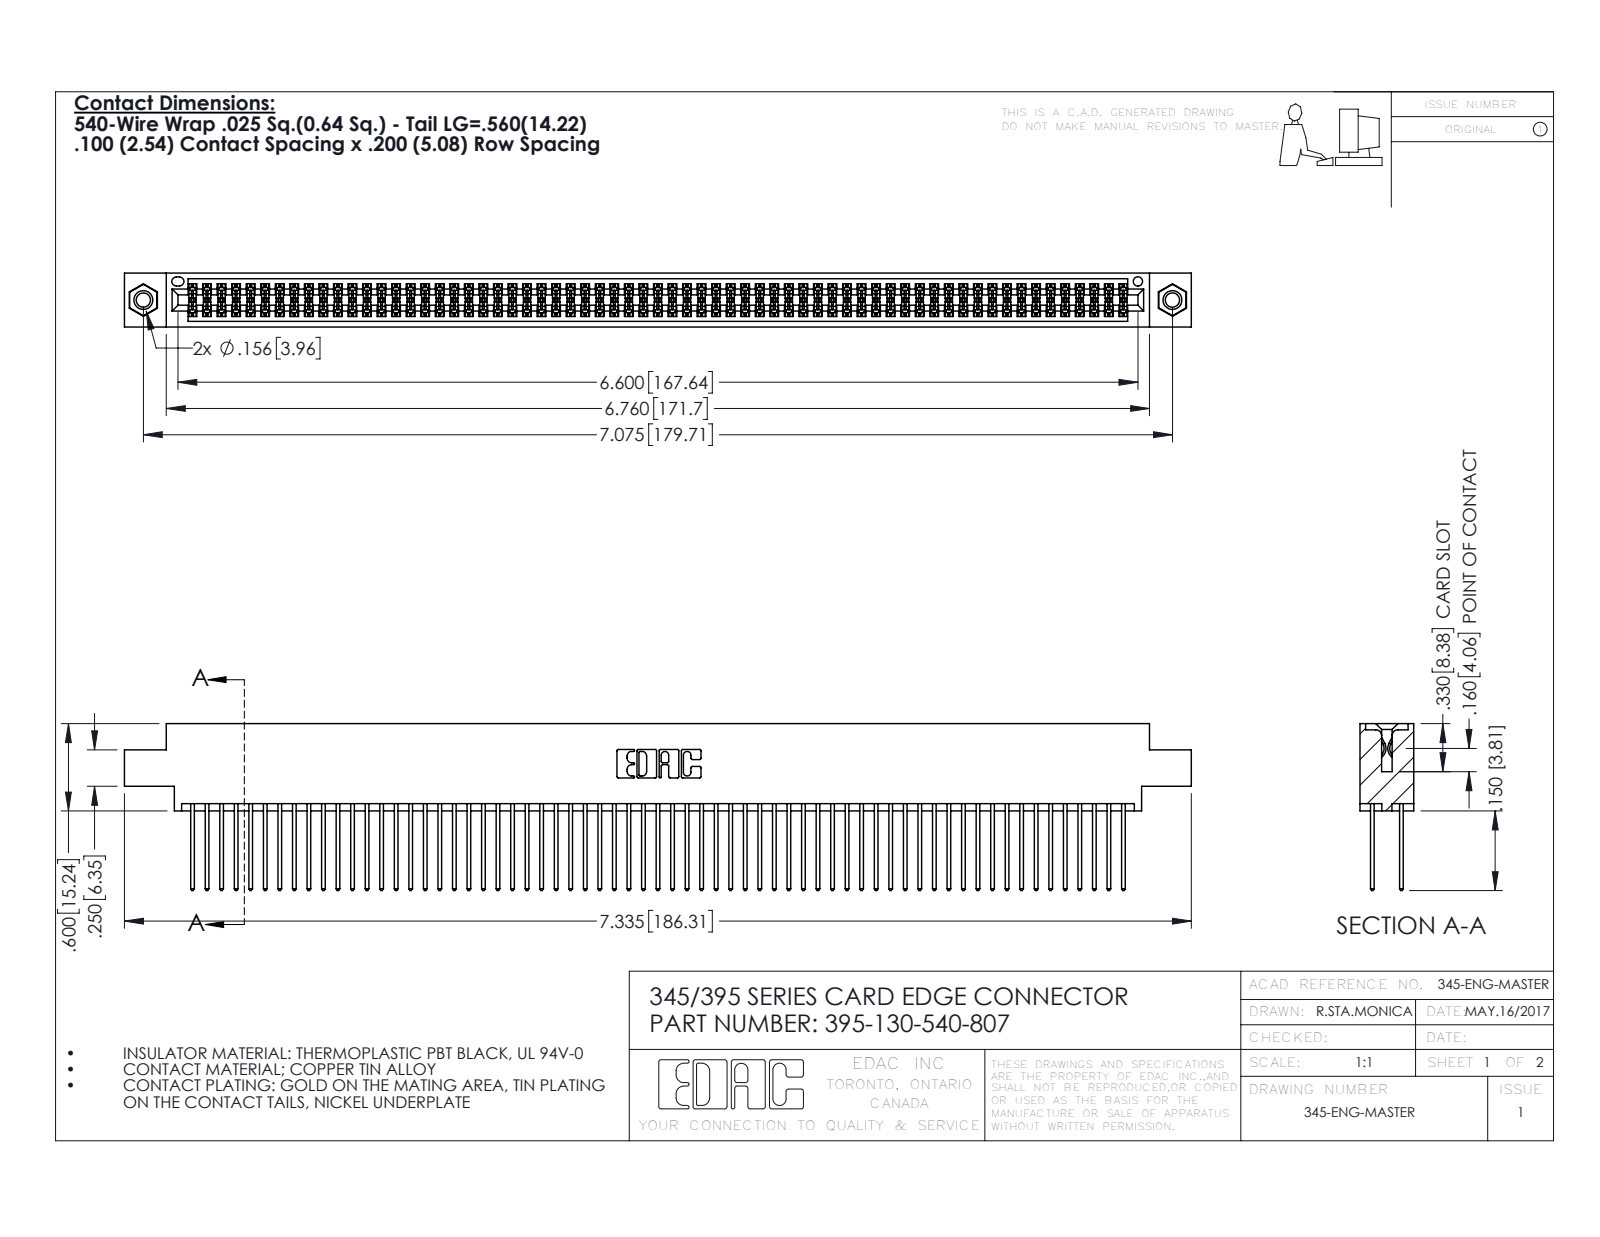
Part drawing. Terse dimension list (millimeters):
name: 345-292-001_345-293-140; 395-130-540-807; 345 Part_0.170 Offset - 0.156 Dia-TI; 345-250-001_345-250-005-103
written by: SolidWorks 2016 (CONFIG_CONTROL_DESIGN)
unit: mm
bodies: 133 solids, 6690 faces (4406 planar, 2268 cylindrical, 16 other)
size: 186.3 × 29.1 × 9.4
volume: 18 680 mm³; area: 30 510 mm²
holes: 2× ⌀2.5, 2× ⌀3.2, 2× ⌀4, 1× ⌀1.6
bosses: 2× ⌀3.9
rounds: 195× R0.2, 130× R0.3, 22× R0.3, 6× R0.2, 6× R0.8, 3× R0.7, 2× R0.4, 2× R0.5
face distances: 1.8, 7.6, 5.1, 2.5, 6.9, 0.6, 9.4, 5.7, 4.4, 3.8
hole spacings: 6.9, 173.7, 179.7
